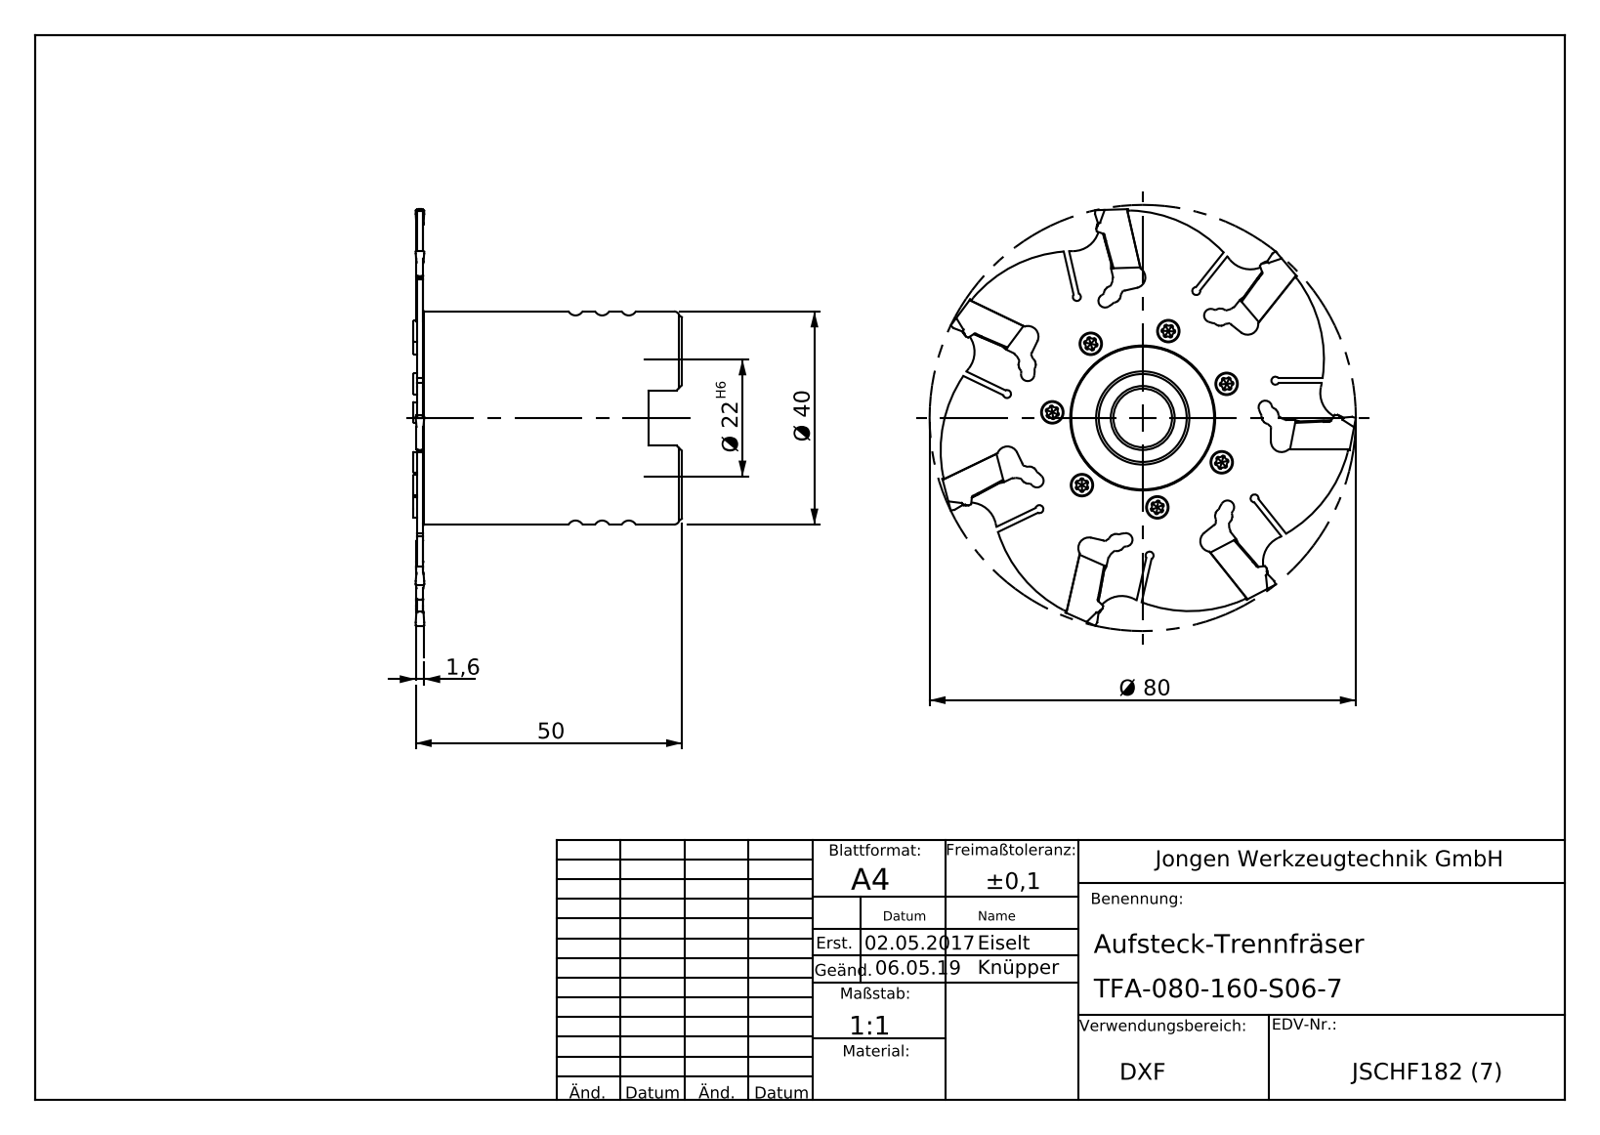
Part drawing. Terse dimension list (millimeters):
name: JSCHF182_1 pk; TFA-080-160-S06-7; JSCHF182 pk_Kontrolle
written by: SolidWorks 2018 (AUTOMOTIVE_DESIGN)
unit: mm
bodies: 2 solids, 167 faces (20 planar, 69 cylindrical, 78 other)
size: 80 × 80 × 50
volume: 54 315 mm³; area: 21 018 mm²
holes: 7× ⌀2.5, 7× ⌀3.2, 1× ⌀11, 1× ⌀16.5, 1× ⌀22, 1× ⌀22.15, 1× ⌀22.3, 1× ⌀27, 1× ⌀44.12
bosses: 1× ⌀80, 1× ⌀40
rounds: 7× R1.25, 7× R7.14
face distances: 1.6, 1.4, 1.2, 48.4, 48.6, 49.8, 50, 20, 28.4, 28.6
hole spacings: 17, 26.59, 33.15, 14.76, 14.75, 33.16, 17.01, 26.58
